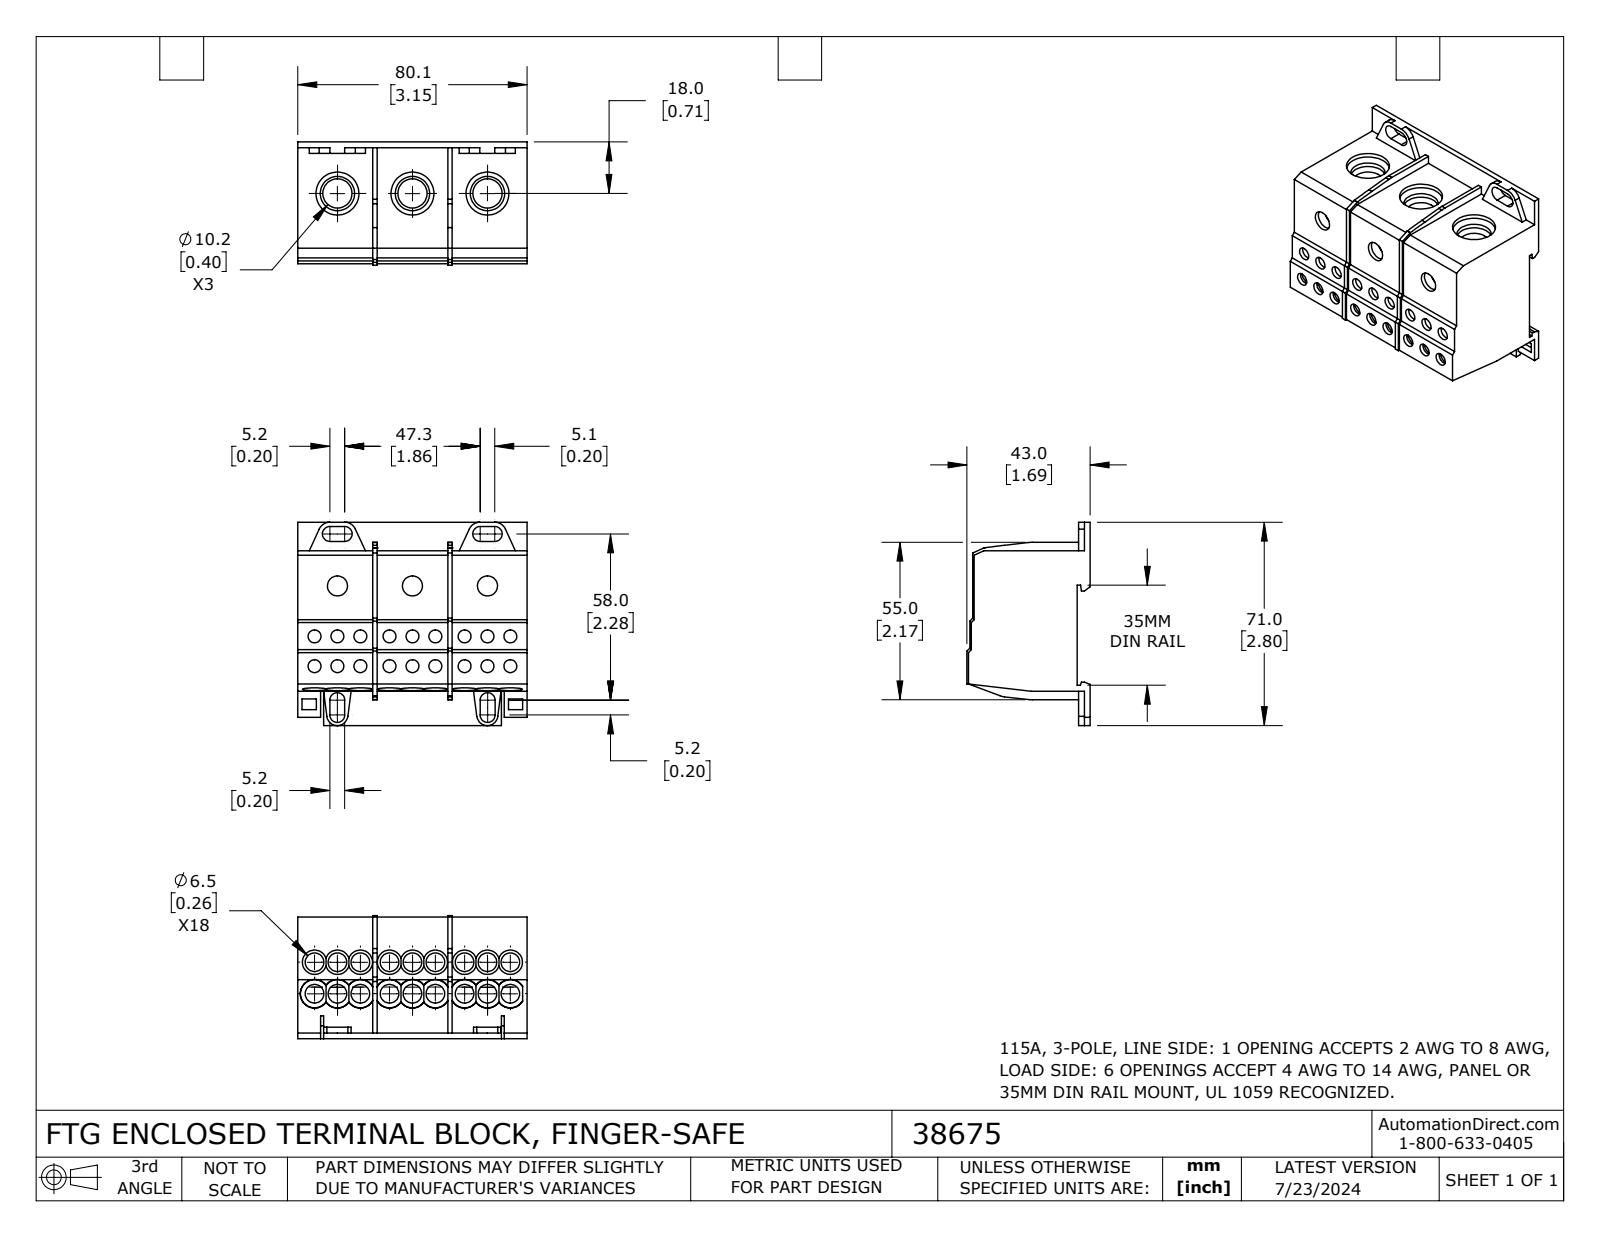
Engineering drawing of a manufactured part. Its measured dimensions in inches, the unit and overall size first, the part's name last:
Units: inches
Overall size (bounding box): 3.154 × 2.795 × 1.693
Round holes (diameter × count): ⌀0.256 ×36, ⌀0.177 ×18, ⌀0.335 ×6, ⌀0.276 ×3, ⌀0.402 ×3, ⌀0.413 ×3, ⌀0.472 ×3, ⌀0.52 ×3, ⌀0.591 ×3, ⌀0.394 ×1
Partial cylindrical surfaces — rounded edges, fillets, slot ends (radius × count): R0.187 ×14, R0.102 ×9, R0.197 ×8, R0.161 ×4, R0.167 ×3, R0.146 ×2, R0.533 ×2, R0.264 ×1
Main face-to-face distances: 0.177, 0.079, 1.594, 0.039, 3.154, 1.417, 0.059, 0.098, 1.516, 0.02
Hole centre spacings: 1.031, 0.315, 2.063, 0.717, 1.346, 0.517, 0.535, 0.63
Volume: 7.611 in³ · Surface area: 55.3 in²
Bodies: 1 solid, 604 faces (261 planar, 251 cylindrical, 92 other)
Part name (STEP PRODUCT): 38675
STEP written by: SolidWorks 2023 (CONFIG_CONTROL_DESIGN)
